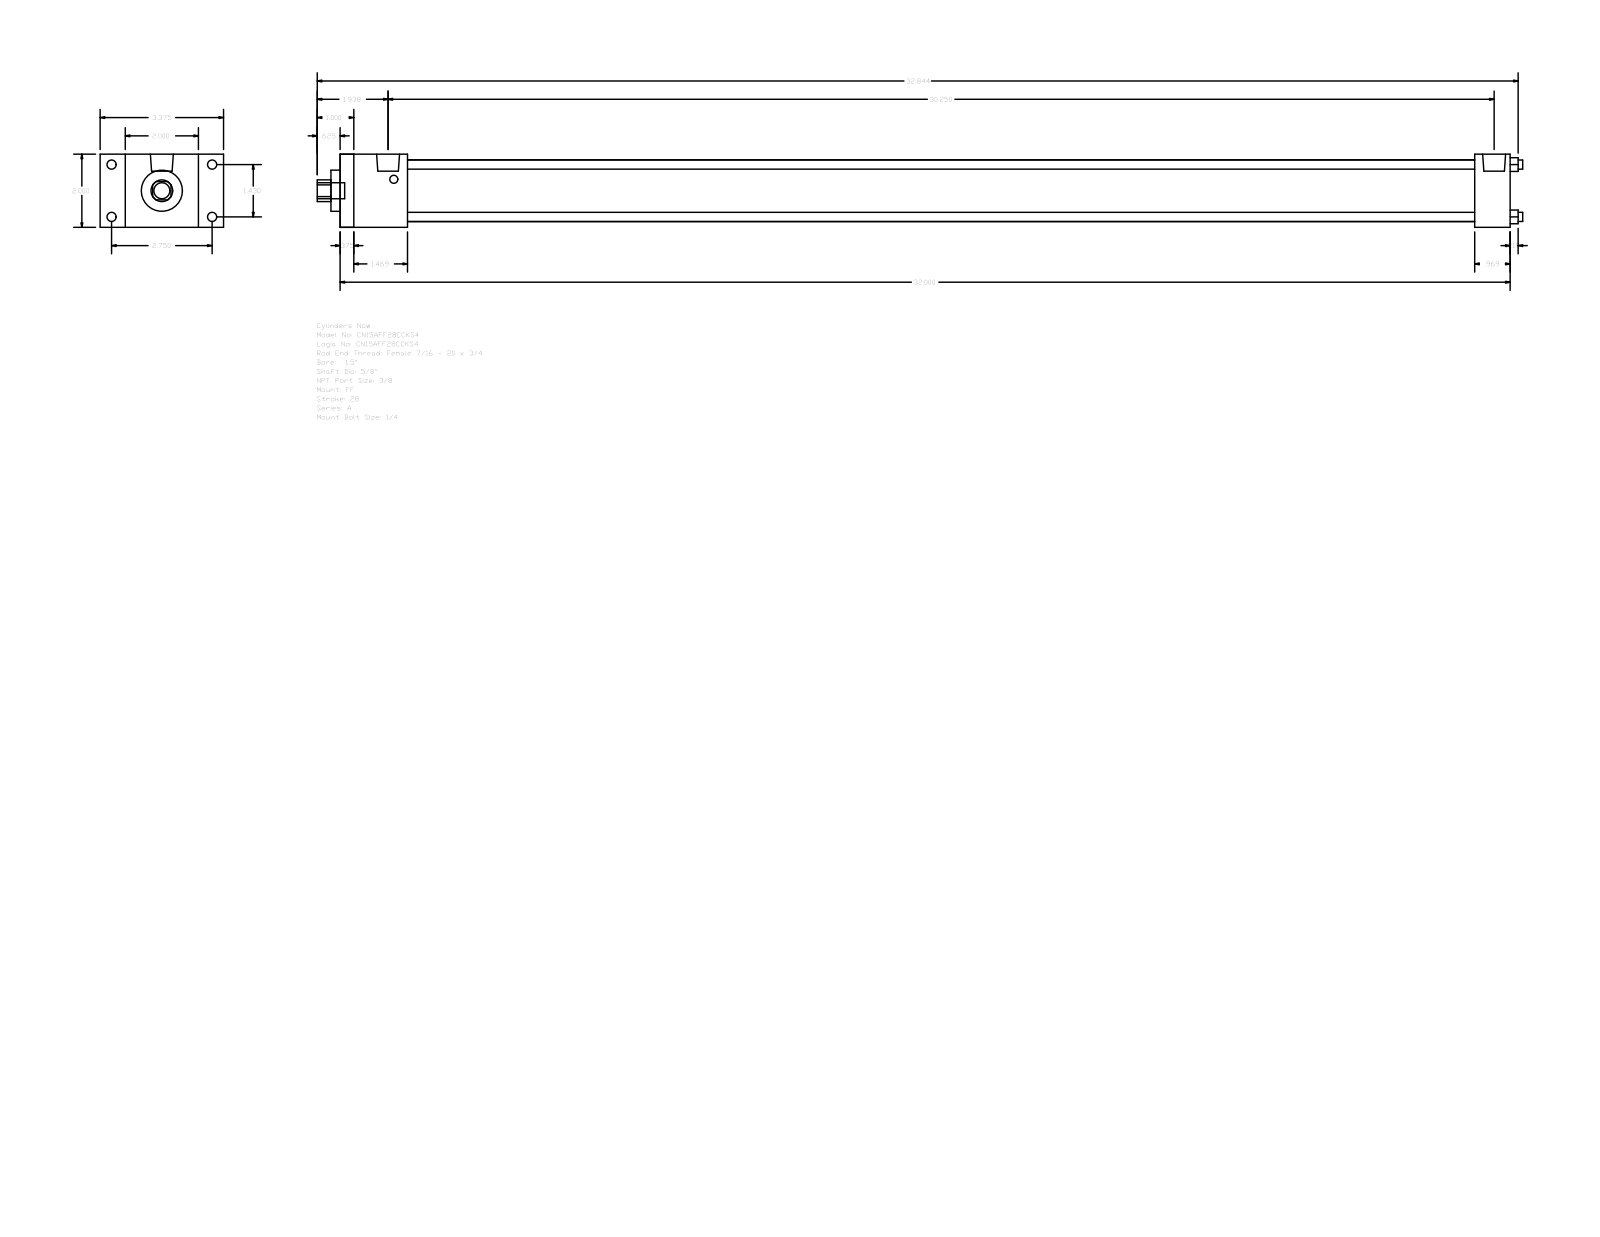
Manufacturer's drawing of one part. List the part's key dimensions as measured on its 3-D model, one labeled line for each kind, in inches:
Part name (STEP PRODUCT): A_FF__0150_0.625
STEP written by: GSSL Pune (CONFIG_CONTROL_DESIGN)
Units: inches
Bodies: 0 solids, 92 faces (64 planar, 28 cylindrical, 0 other)
Overall size (bounding box): 32.969 × 3.375 × 2
Round holes (diameter × count): ⌀0.25 ×4, ⌀0.625 ×1, ⌀1.125 ×1, ⌀1.69 ×1
Round bosses / shafts (diameter × count): ⌀0.25 ×4, ⌀0.219 ×4, ⌀0.627 ×2, ⌀0.437 ×1
Partial cylindrical surfaces — rounded edges, fillets, slot ends (radius × count): R0.297 ×1
Main face-to-face distances: 2, 32, 0.375, 31.625, 1.844, 31.031, 1.469, 30.656, 29.187, 30.156
Hole centre spacings: 1.011, 1.43, 2.022
